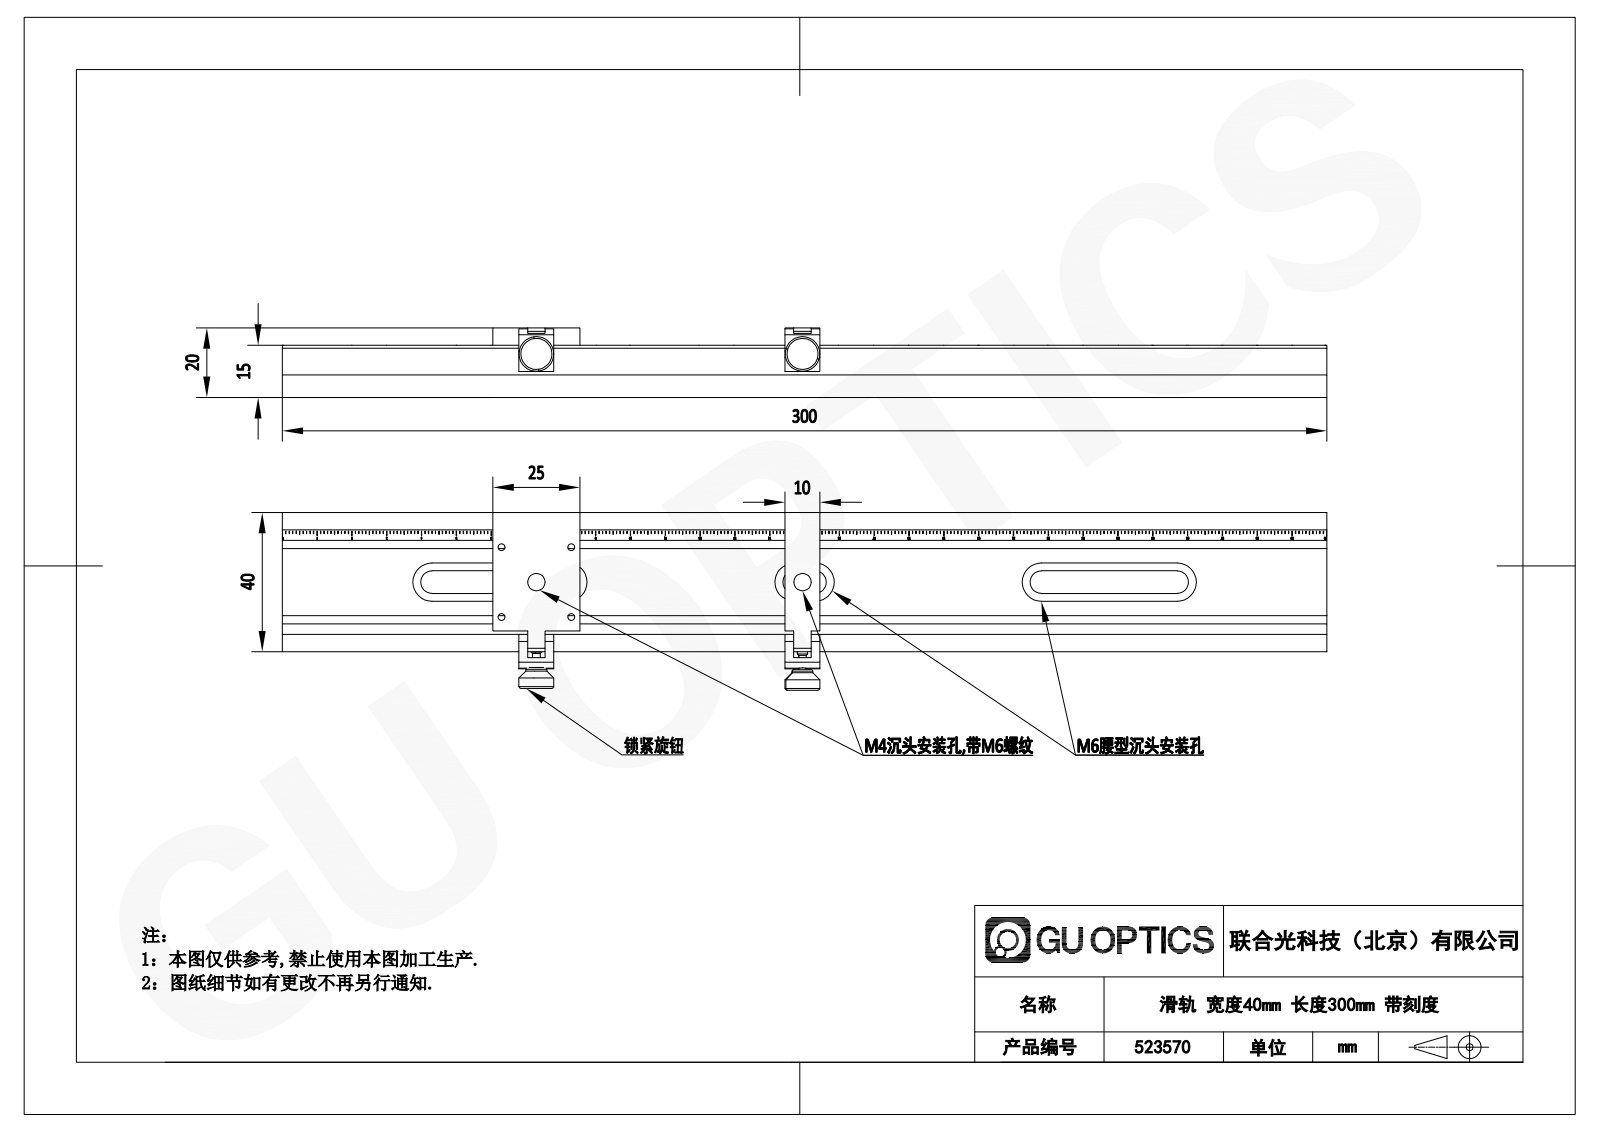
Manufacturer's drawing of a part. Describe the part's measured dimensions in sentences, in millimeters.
The part is named "523570". Its 3-D file was written by "SolidWorks 2020 (CONFIG_CONTROL_DESIGN)". It is 8 solids with 2800 faces: 2176 planar, 83 cylindrical and 541 other. Overall it measures 300 by 51.03 by 20 millimeters. Its volume is 117 536 cubic millimeters and its surface area 46 684 square millimeters. Round holes: 4 of diameter 2.05, 2 of diameter 2.5, 2 of diameter 3.2, 2 of diameter 5, 2 of diameter 8, 1 of diameter 1.5, 1 of diameter 2. Round bosses or shafts: 2 of diameter 10, 2 of diameter 6, 2 of diameter 3, 2 of diameter 2.2. Partial cylindrical surfaces (rounded edges, fillets, slot ends): 6 of radius 3.25, 6 of radius 5.5, 1 of radius 1.25, 1 of radius 2.5, 1 of radius 4.5, 1 of radius 12.5. The main face-to-face distances are 6, 14.5, 0.5, 6.5, 15, 5, 8.5, 40, 8, 9.5. The hole center spacings are 14.14, 20, 28.28, 67.16, 76.41, 86.99.
